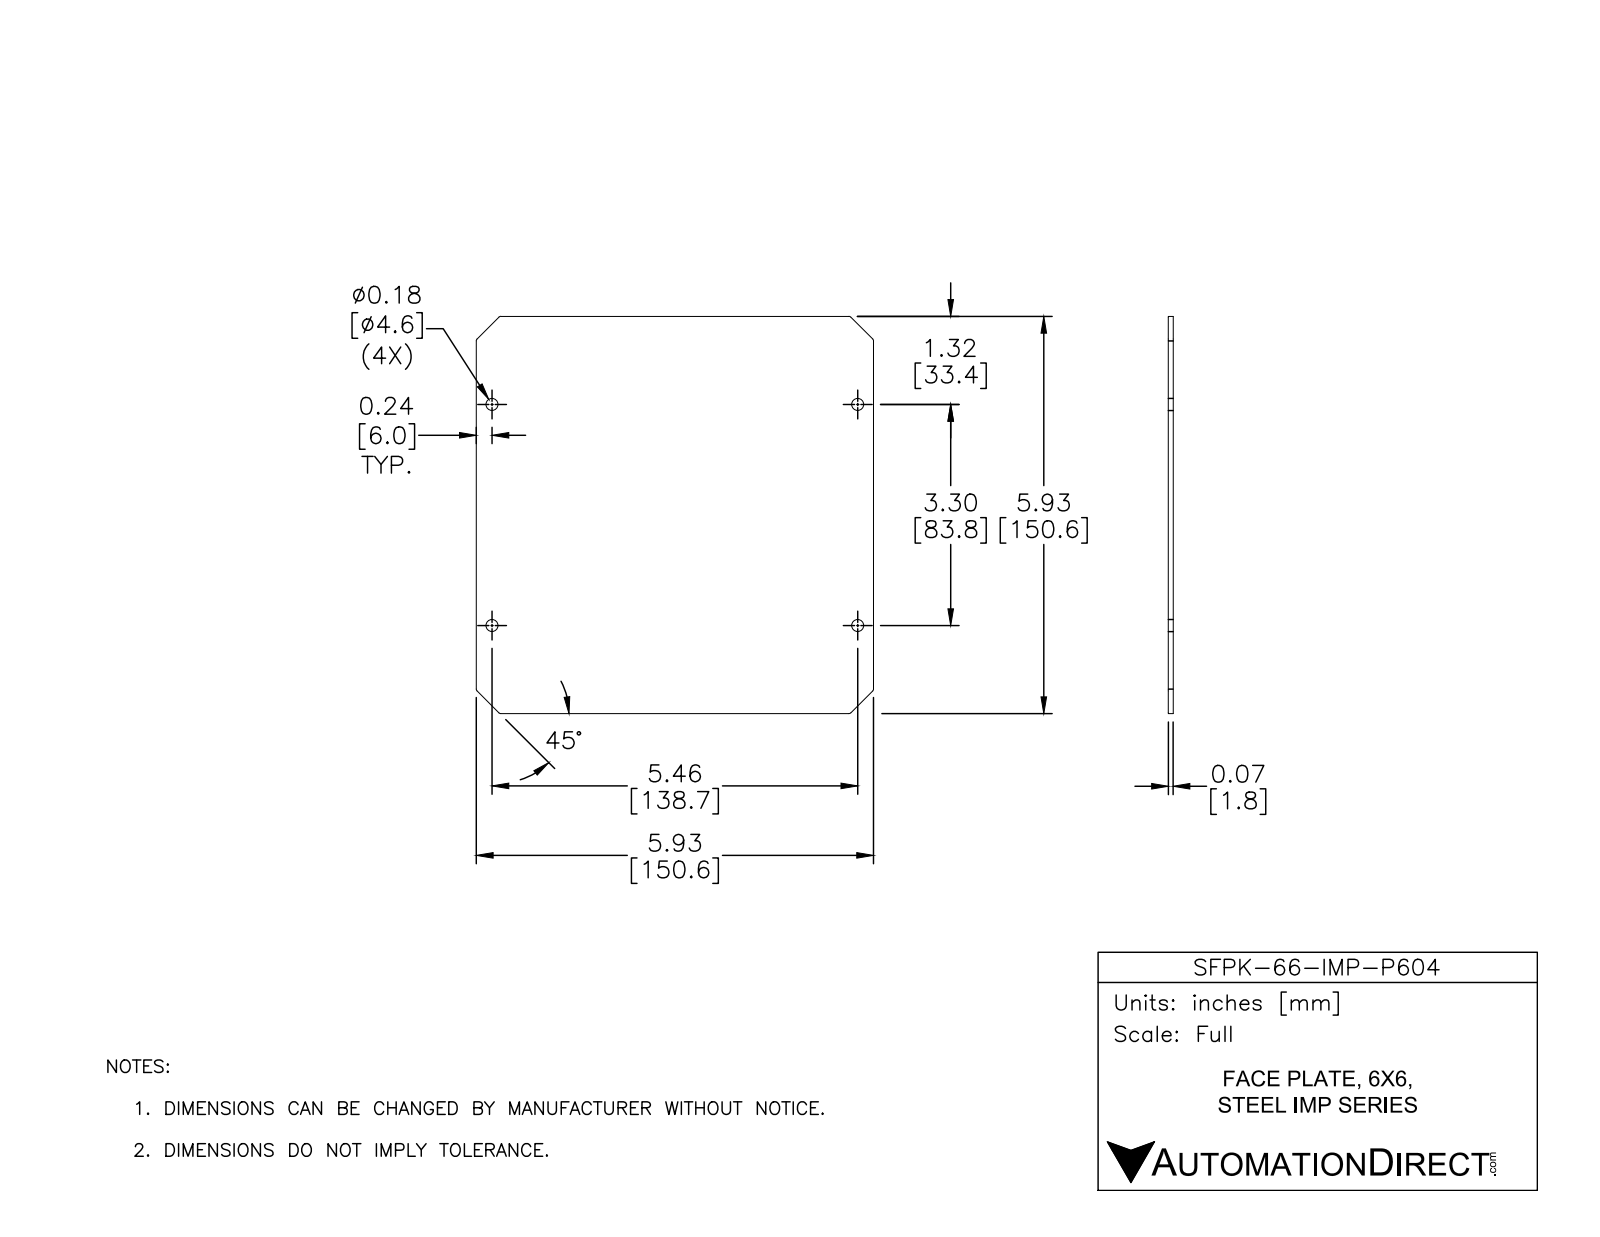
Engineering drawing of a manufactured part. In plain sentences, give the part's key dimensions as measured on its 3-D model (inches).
The part is named "SFPK66-IMP-P604". Its 3-D file was written by "SolidWorks 2016 (AUTOMOTIVE_DESIGN)". It is 1 solid with 26 faces: 10 planar, 16 cylindrical and 0 other. Overall it measures 5.93 by 5.93 by 0.064 inches. Its volume is 2.232 cubic inches and its surface area 71.25 square inches. Round holes: 4 of diameter 0.18. Partial cylindrical surfaces (rounded edges, fillets, slot ends): 8 of radius 0.04. The main face-to-face distances are 0.064, 5.93, 7.89. The hole center spacings are 3.3, 5.46, 6.38.
